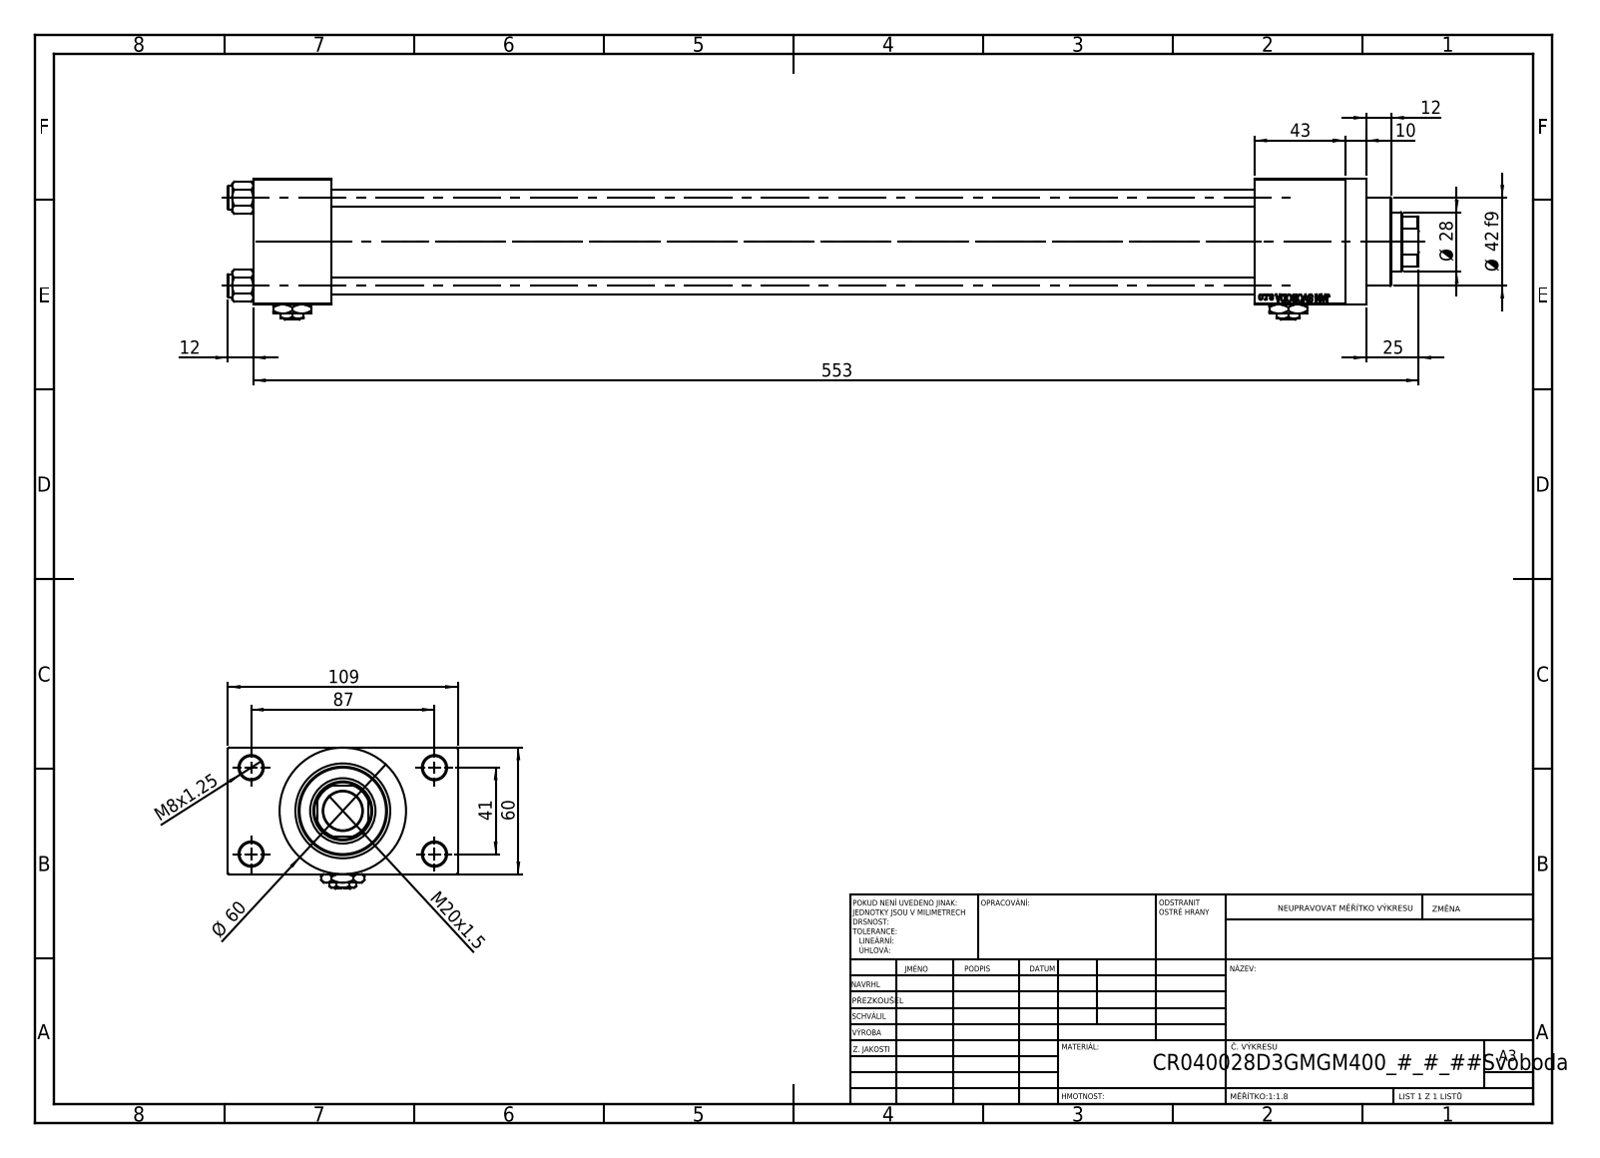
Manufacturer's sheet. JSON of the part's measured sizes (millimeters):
{"part_name": "V215CR_D_TYCINKA; V215_VC_A; V215CR_VCP_D; NUT_M5_D (+2 more)", "step_written_by": "SolidWorks 2019 (CONFIG_CONTROL_DESIGN)", "units": "millimeters", "bodies": {"solids": 13, "faces": 1205, "planar": 546, "cylindrical": 99, "other": 560}, "overall_size": [565, 109, 67], "volume_mm3": 991405, "surface_area_mm2": 305959, "round_holes": [[8, 4], [11, 4], [16.66, 4], [24, 4], [7, 3], [18.5, 1], [28, 1], [31, 1], [40, 1], [45, 1]], "round_bosses_or_shafts": [[11, 4], [60, 1], [46, 1], [42, 1]], "partial_cylinders_radius": [[13.5, 1]], "face_to_face_distances": [60, 24.5, 438, 84.5, 37, 475, 518, 481, 43, 109], "hole_center_spacings": [22.65, 29.49, 41.7, 47.15, 48.09, 64.35, 76.49, 41]}
